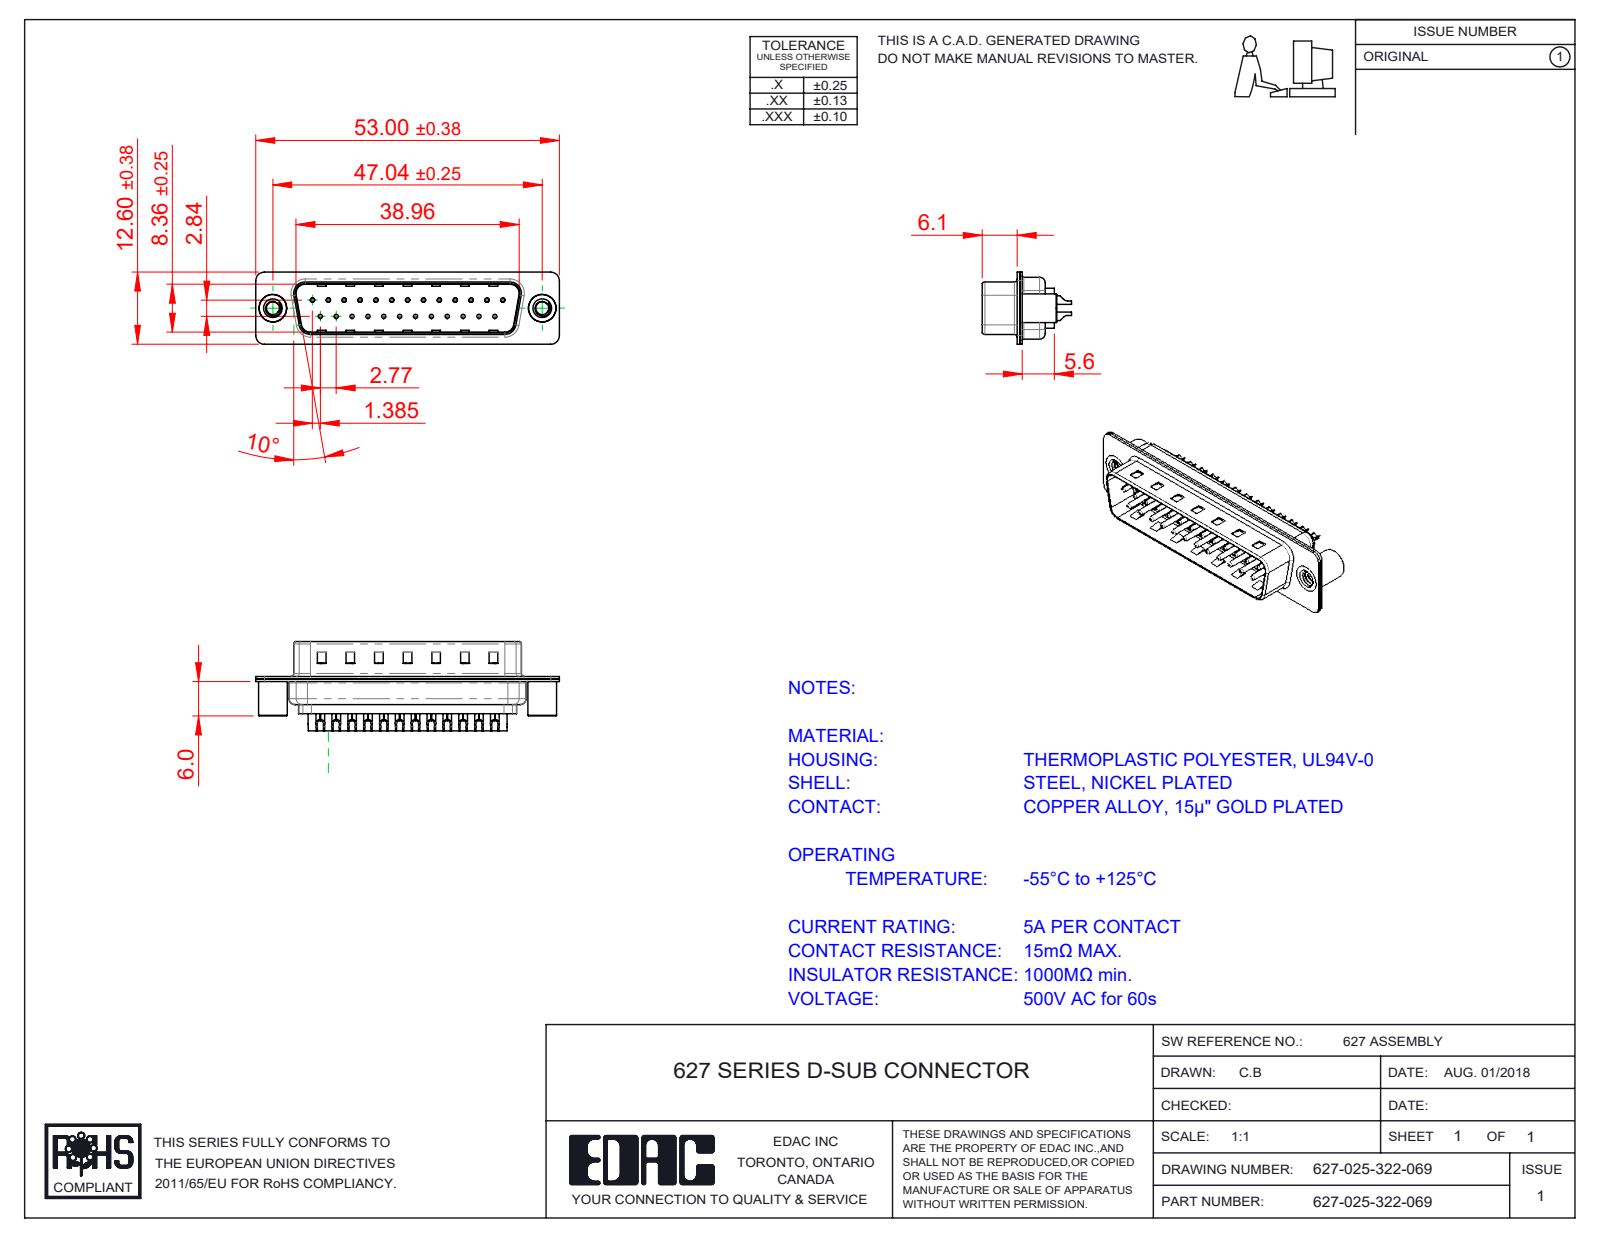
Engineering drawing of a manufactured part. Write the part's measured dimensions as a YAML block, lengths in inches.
part_name: "627 Contact Row 2_22L; 627-025-322-069; 627 Contact Row 1_22L; 627 Shell Front_25 Contacts (+3 more)"
step_written_by: "SolidWorks 2020 (CONFIG_CONTROL_DESIGN)"
units: inches
bodies: {solids: 30, faces: 1998, planar: 521, cylindrical: 882, other: 595}
overall_size: [2.087, 0.604, 0.496]
volume: 0.17
surface_area: 12.47
round_holes:
  - {diameter: 0.014, count: 25}
  - {diameter: 0.043, count: 25}
  - {diameter: 0.063, count: 25}
  - {diameter: 0.089, count: 2}
  - {diameter: 0.157, count: 2}
  - {diameter: 0.189, count: 2}
round_bosses_or_shafts:
  - {diameter: 0.079, count: 25}
  - {diameter: 0.059, count: 25}
  - {diameter: 0.03, count: 25}
  - {diameter: 0.197, count: 2}
  - {diameter: 0.193, count: 2}
partial_cylinders:
  - {radius: 0.059, count: 16}
  - {radius: 0.079, count: 12}
  - {radius: 0.02, count: 8}
  - {radius: 0.063, count: 8}
  - {radius: 0.039, count: 6}
  - {radius: 0.01, count: 4}
  - {radius: 0.024, count: 4}
  - {radius: 0.026, count: 4}
face_to_face_distances: [0.016, 0.018, 0.032, 0.377, 0.345, 0.035, 0.059, 0.256, 0.055, 0.238]
hole_center_spacings: [0.124, 0.327, 0.109, 0.218, 0.436, 0.654, 0.198, 0.198]
